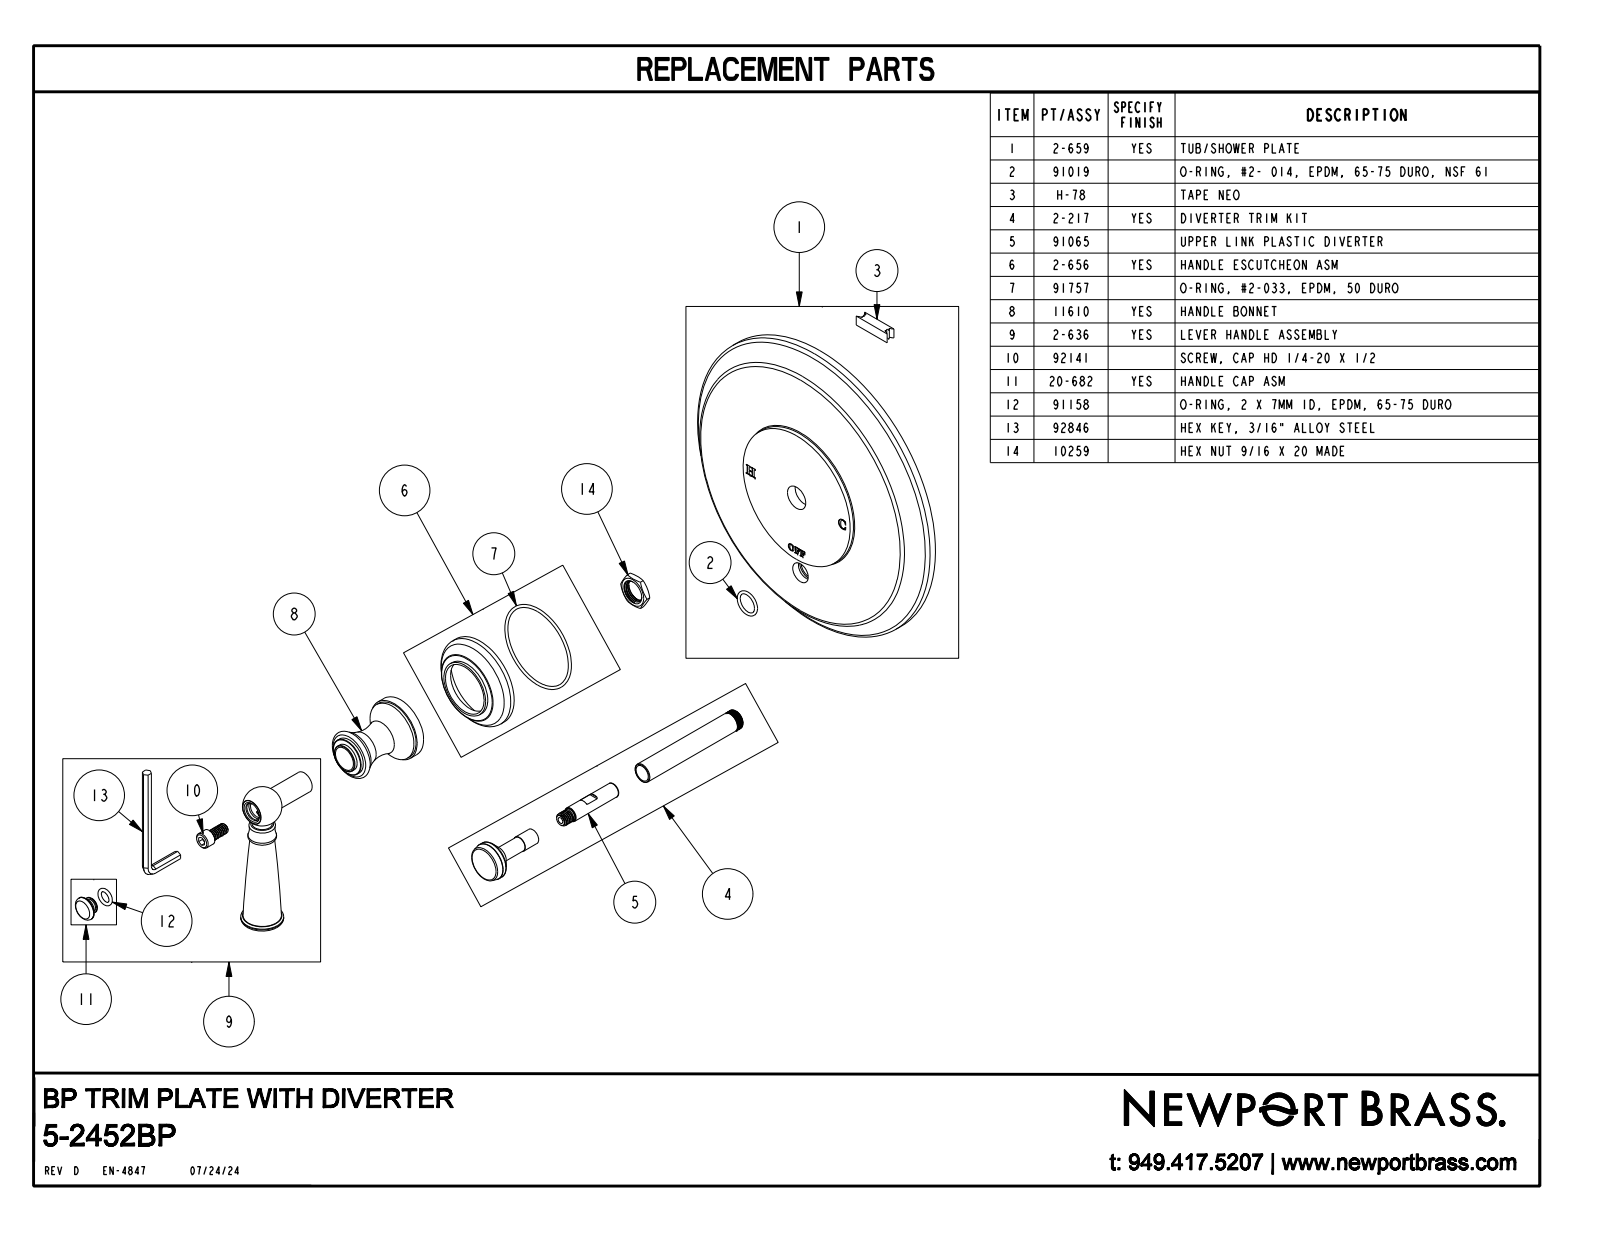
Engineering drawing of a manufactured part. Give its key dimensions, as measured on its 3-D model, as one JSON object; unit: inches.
{"part_name": "5-2452BP", "step_written_by": "CREO PARAMETRIC BY PTC INC, 2018400 (CONFIG_CONTROL_DESIGN)", "units": "inches", "bodies": {"solids": 1, "faces": 234, "planar": 45, "cylindrical": 26, "other": 163}, "overall_size": [7.5, 7.5, 4.072], "volume_in3": 30.65, "surface_area_in2": 118.6, "round_bosses_or_shafts": [[0.9, 2], [7.5, 1], [2.2, 1], [1.49, 1], [1.42, 1], [0.983, 1], [0.66, 1], [0.56, 1]], "face_to_face_distances": [0.625, 0.75, 0.125, 1.977, 1.352, 1.227, 1.18, 0.555, 0.43, 0.797]}
